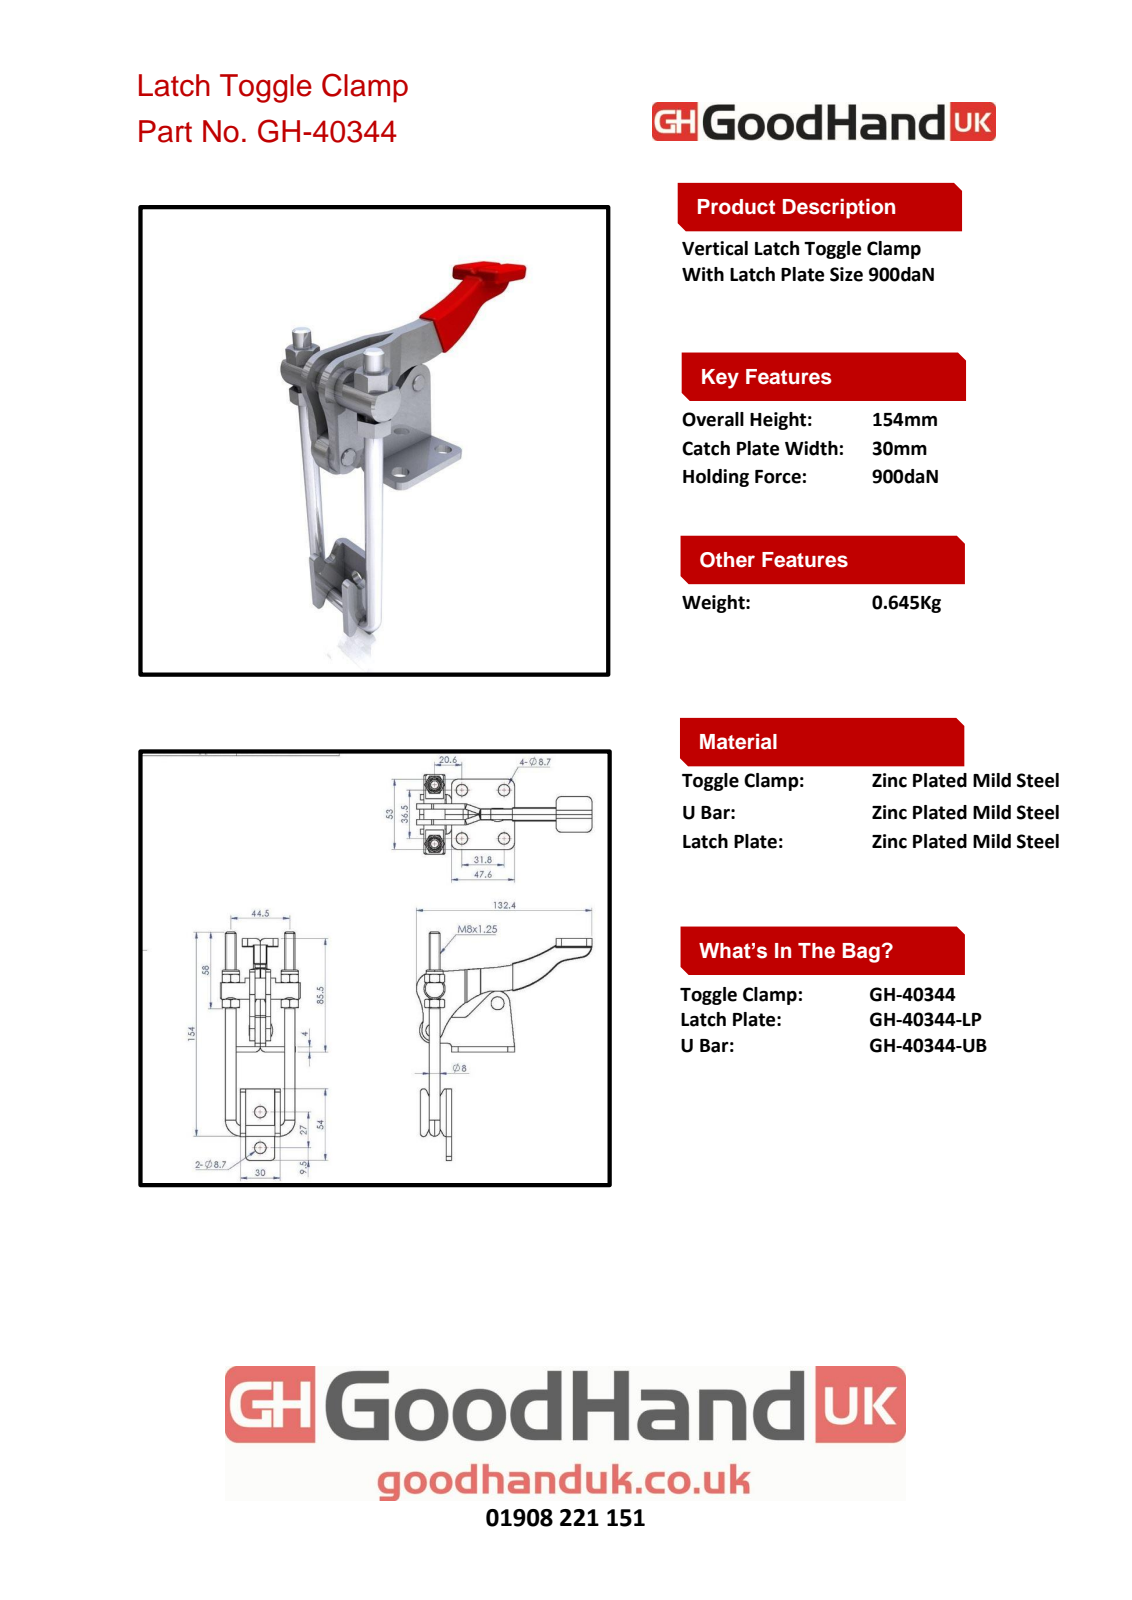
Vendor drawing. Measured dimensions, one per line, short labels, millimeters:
name: Group1^GH-40344(簡化); Group2^GH-40344(簡化); 44034444-1^GH-40344(簡化); Group3^GH-40344(簡化) (+2 more)
written by: SolidWorks 2016 (AUTOMOTIVE_DESIGN)
unit: mm
bodies: 8 solids, 435 faces (168 planar, 178 cylindrical, 89 other)
size: 172.25 × 132.4 × 60.3
volume: 90 787 mm³; area: 51 817 mm²
holes: 6× ⌀8.7, 2× ⌀6.8, 2× ⌀8.5, 2× ⌀9, 1× ⌀6, 1× ⌀6.3, 1× ⌀16
bosses: 3× ⌀8, 2× ⌀12.4, 1× ⌀5.92
rounds: 10× R0.1, 10× R4.1, 6× R0.5, 6× R3, 5× R2.5, 5× R5, 4× R3.1, 4× R4
face distances: 4, 8, 3, 19, 12, 1, 16, 0.9, 7, 13
hole spacings: 20.98, 31.8, 36.5, 45.44, 48.41, 52.55, 66.23, 27
